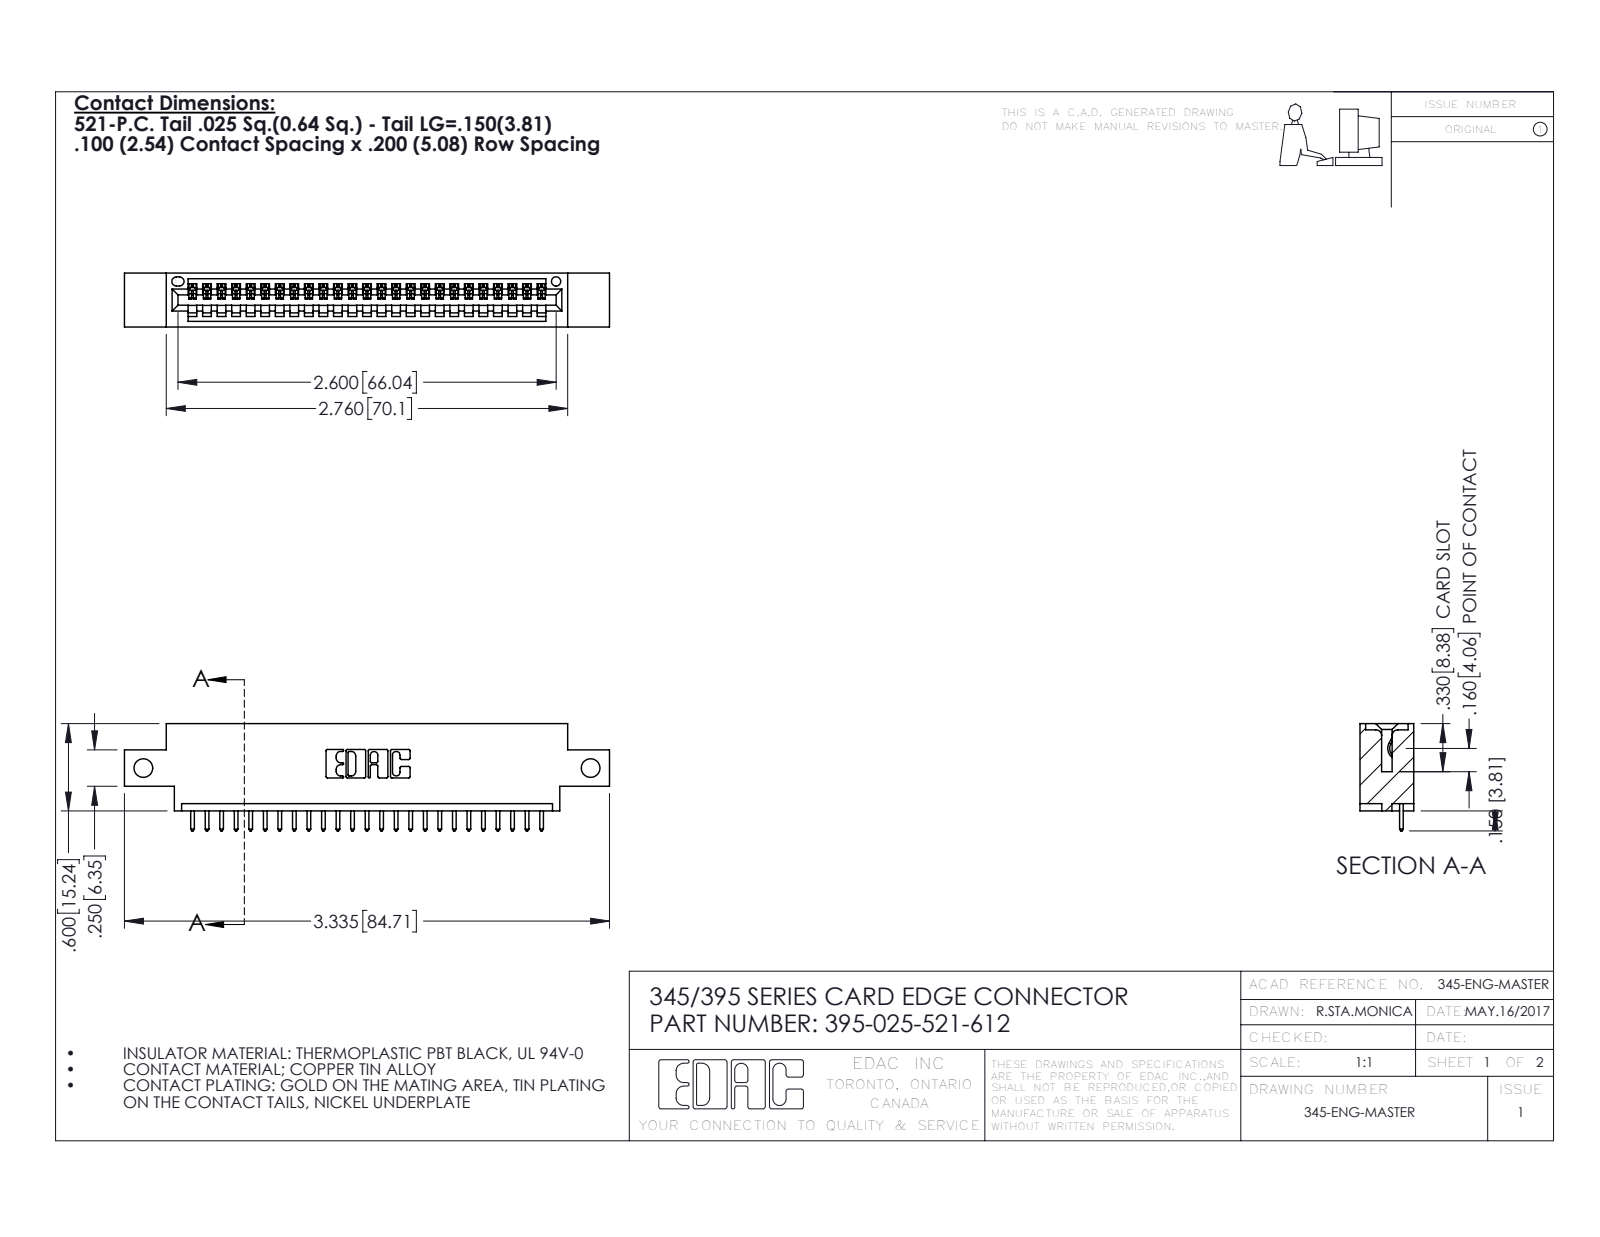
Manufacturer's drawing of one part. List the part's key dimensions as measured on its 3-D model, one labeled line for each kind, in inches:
Part name (STEP PRODUCT): 395-025-521-612; 345-292-001_345-293-121; 345 Part_0.170 Offset - Side Mount
STEP written by: SolidWorks 2016 (CONFIG_CONTROL_DESIGN)
Units: inches
Bodies: 26 solids, 1580 faces (1084 planar, 496 cylindrical, 0 other)
Overall size (bounding box): 3.335 × 0.737 × 0.37
Volume: 0.466 in³ · Surface area: 14.91 in²
Round holes (diameter × count): ⌀0.128 ×2, ⌀0.064 ×1
Partial cylindrical surfaces — rounded edges, fillets, slot ends (radius × count): R0.006 ×50, R0.01 ×50, R0.01 ×22, R0.007 ×6, R0.031 ×6, R0.026 ×3, R0.031 ×2, R0.04 ×2
Main face-to-face distances: 0.072, 0.298, 0.37, 0.2, 0.098, 0.272, 0.025, 0.225, 0.175, 0.149
Hole centre spacings: 3.075
